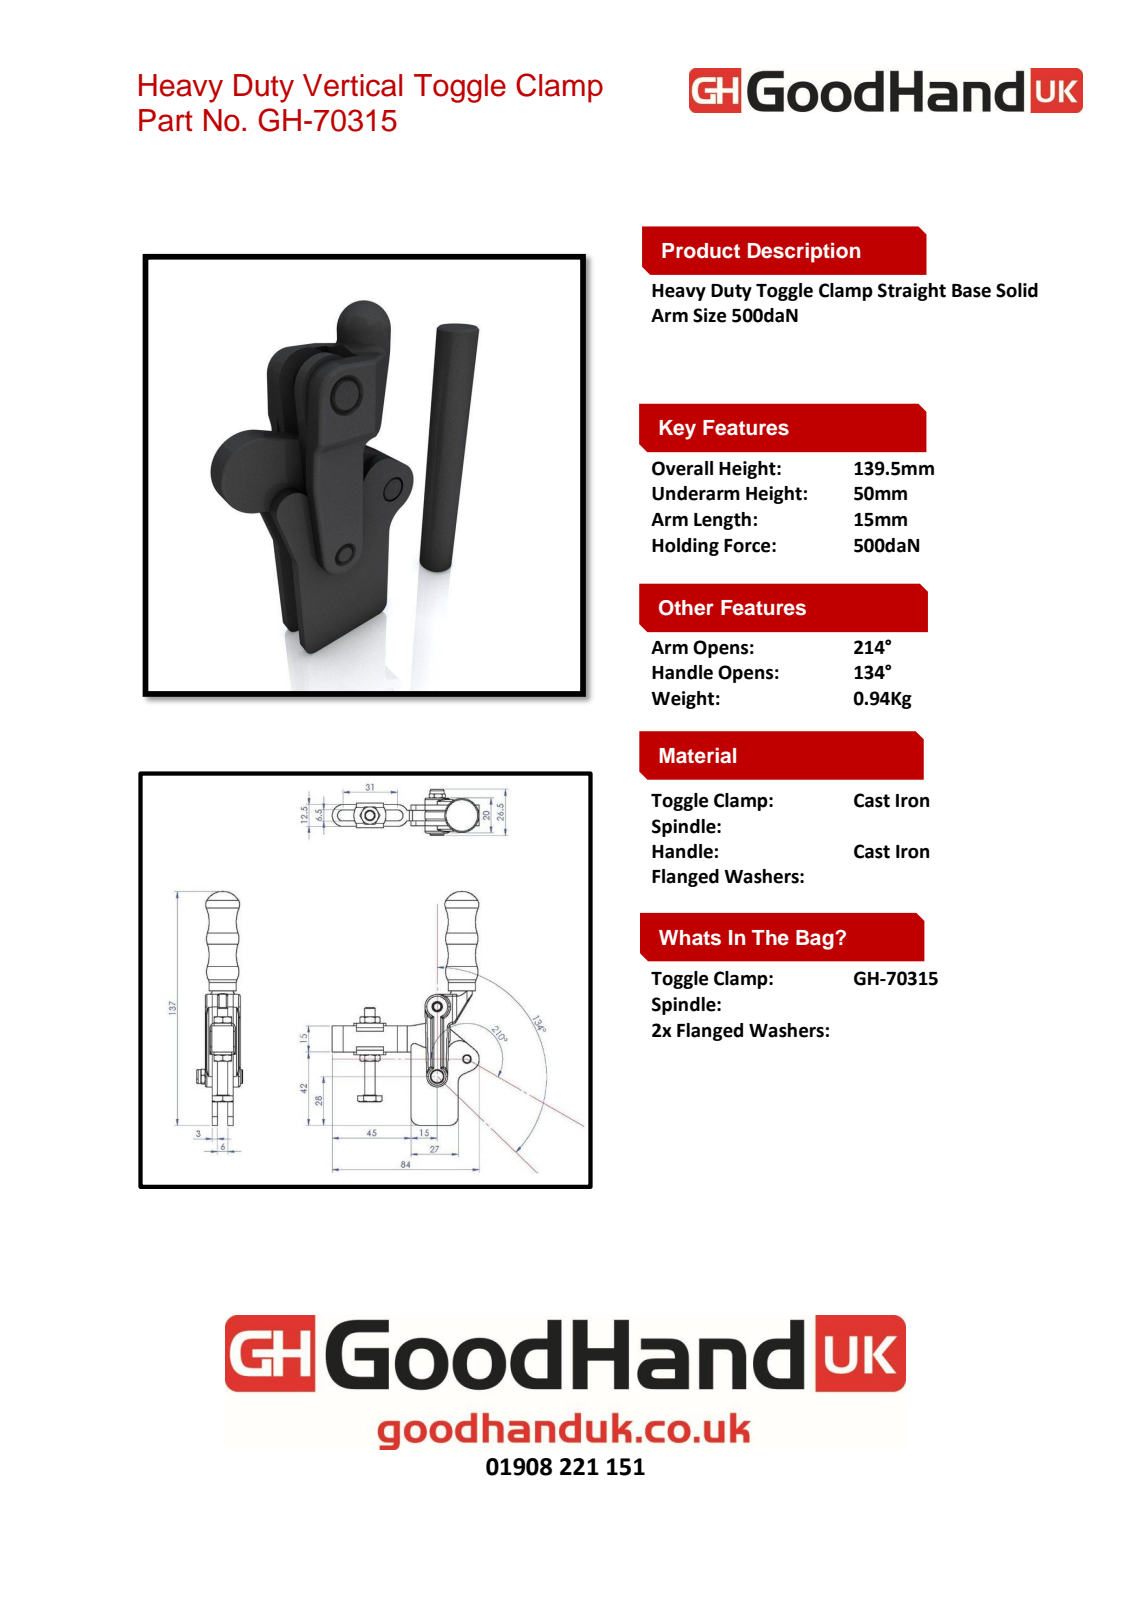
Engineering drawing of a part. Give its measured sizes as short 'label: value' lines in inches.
name: Group1^GH-70315(簡化)-1; Group5^GH-70315(簡化)-1; GH-70315(簡化)-1; 37031008-1^GH-70315(簡化)-1 (+2 more)
written by: SolidWorks 2016 (AUTOMOTIVE_DESIGN)
unit: in
bodies: 5 solids, 223 faces (75 planar, 99 cylindrical, 49 other)
size: 10.441 × 3.121 × 1.638
volume: 7.22 in³; area: 84.69 in²
holes: 3× ⌀0.315, 1× ⌀0.492
bosses: 2× ⌀0.322, 1× ⌀0.748, 1× ⌀0.681, 1× ⌀0.591, 1× ⌀0.472, 1× ⌀0.315, 1× ⌀0.313
rounds: 22× R0.079, 8× R0.197, 2× R0.374, 2× R0.433, 2× R0.453, 1× R0.256, 1× R0.394, 1× R0.472
face distances: 0.189, 0.583, 0.394, 0.772, 0.201, 0.594, 0.783, 0.791, 0.197, 0.591
hole spacings: 1.242, 1.26, 2.5
